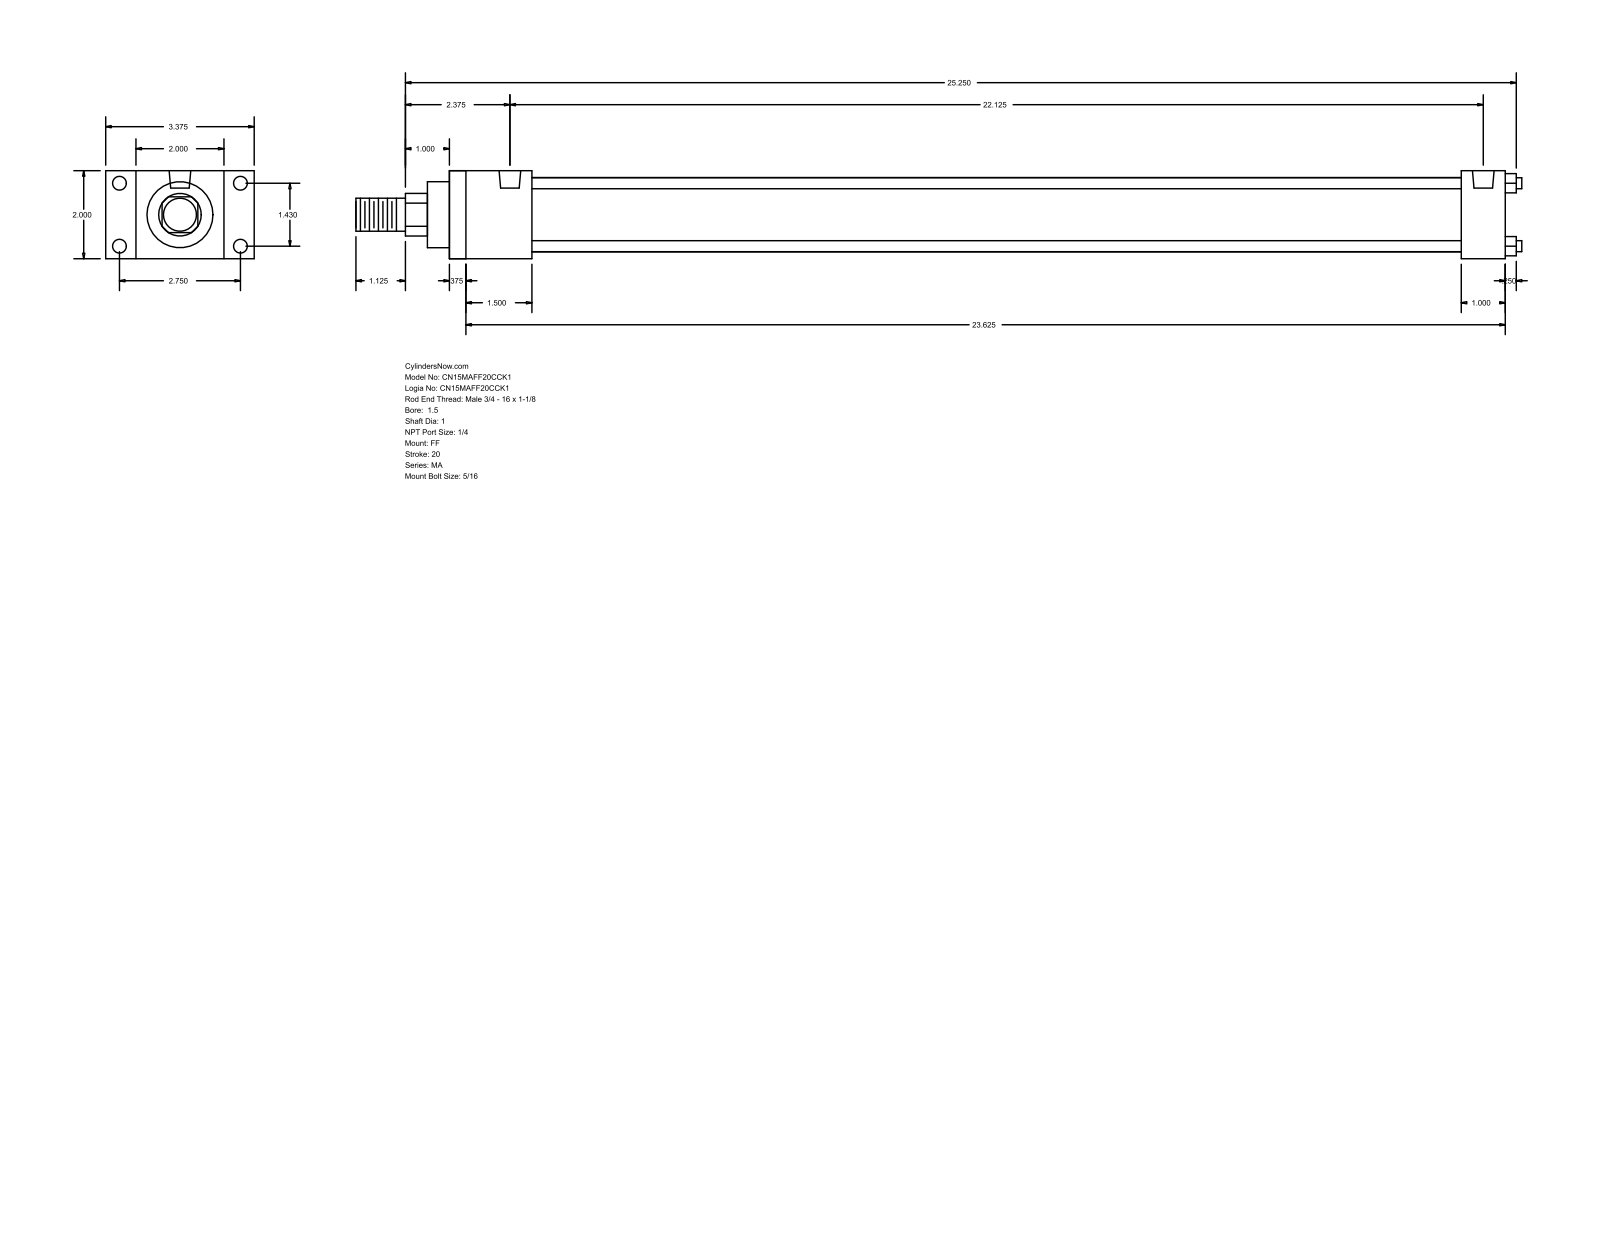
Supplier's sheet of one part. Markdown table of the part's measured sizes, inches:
| quantity | value |
| --- | --- |
| part name | MA_FF__0150_1 |
| STEP written by | GSSL Pune (CONFIG_CONTROL_DESIGN) |
| units | inches |
| bodies | 0 solids, 92 faces (64 planar, 28 cylindrical, 0 other) |
| overall size | 26.5 × 3.375 × 2 |
| round holes (diameter × count) | 0.313 × 8, 0.492 × 2 |
| round bosses / shafts (diameter × count) | 0.25 × 4, 1.69 × 1, 1.5 × 1, 1 × 1, 0.75 × 1 |
| partial cylindrical surfaces (radius × count) | 0.484 × 1 |
| main face-to-face distances | 2, 24, 0.375, 23.625, 1, 1.875, 23, 1.5, 22.625, 21.125 |
| hole center spacings | 1.43, 2.75, 3.099, 22.125 |
